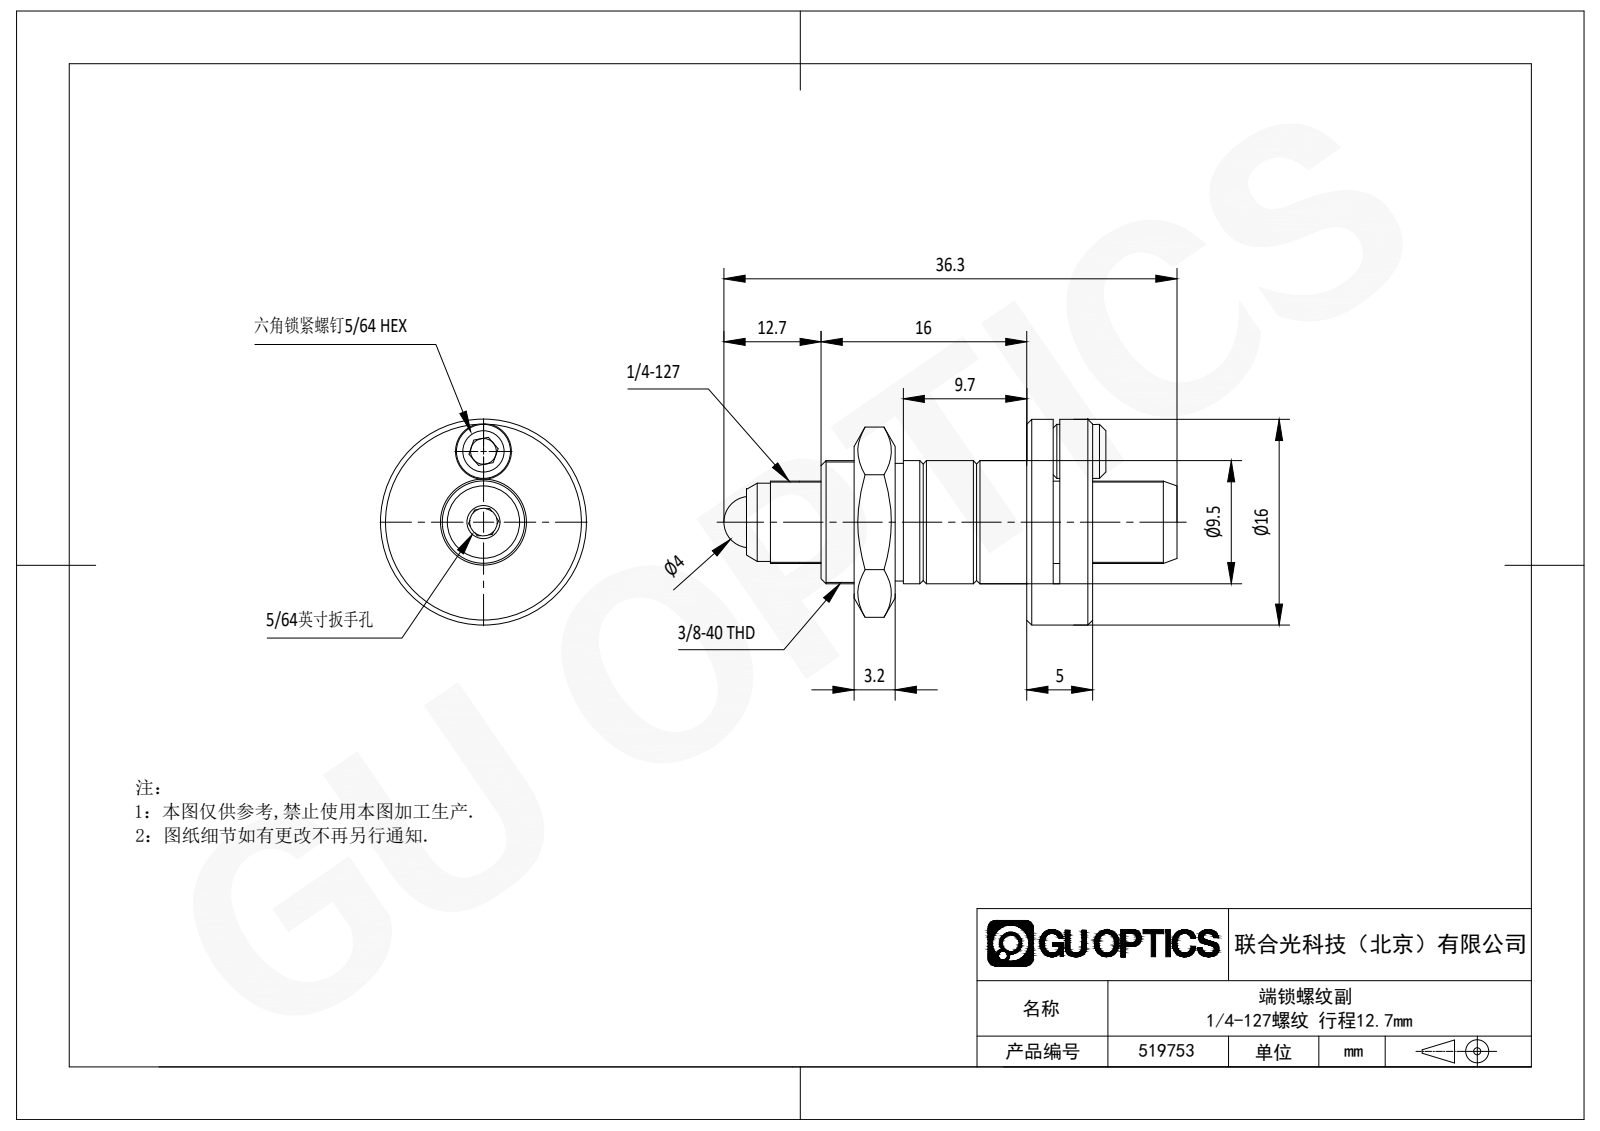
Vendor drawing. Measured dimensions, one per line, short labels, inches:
name: AJS127-0.5H
written by: SolidWorks 2020 (CONFIG_CONTROL_DESIGN)
unit: in
bodies: 1 solid, 91 faces (48 planar, 17 cylindrical, 26 other)
size: 1.43 × 0.63 × 0.63
volume: 0.161 in³; area: 3.422 in²
holes: 1× ⌀0.059, 1× ⌀0.083, 1× ⌀0.26
bosses: 1× ⌀0.63, 1× ⌀0.374, 1× ⌀0.344, 1× ⌀0.25, 1× ⌀0.238, 1× ⌀0.164
rounds: 1× R0.298, 1× R1
face distances: 0.02, 0.1, 0.12, 0.197, 0.097, 0.077, 0.5, 0.605, 0.725, 0.625
